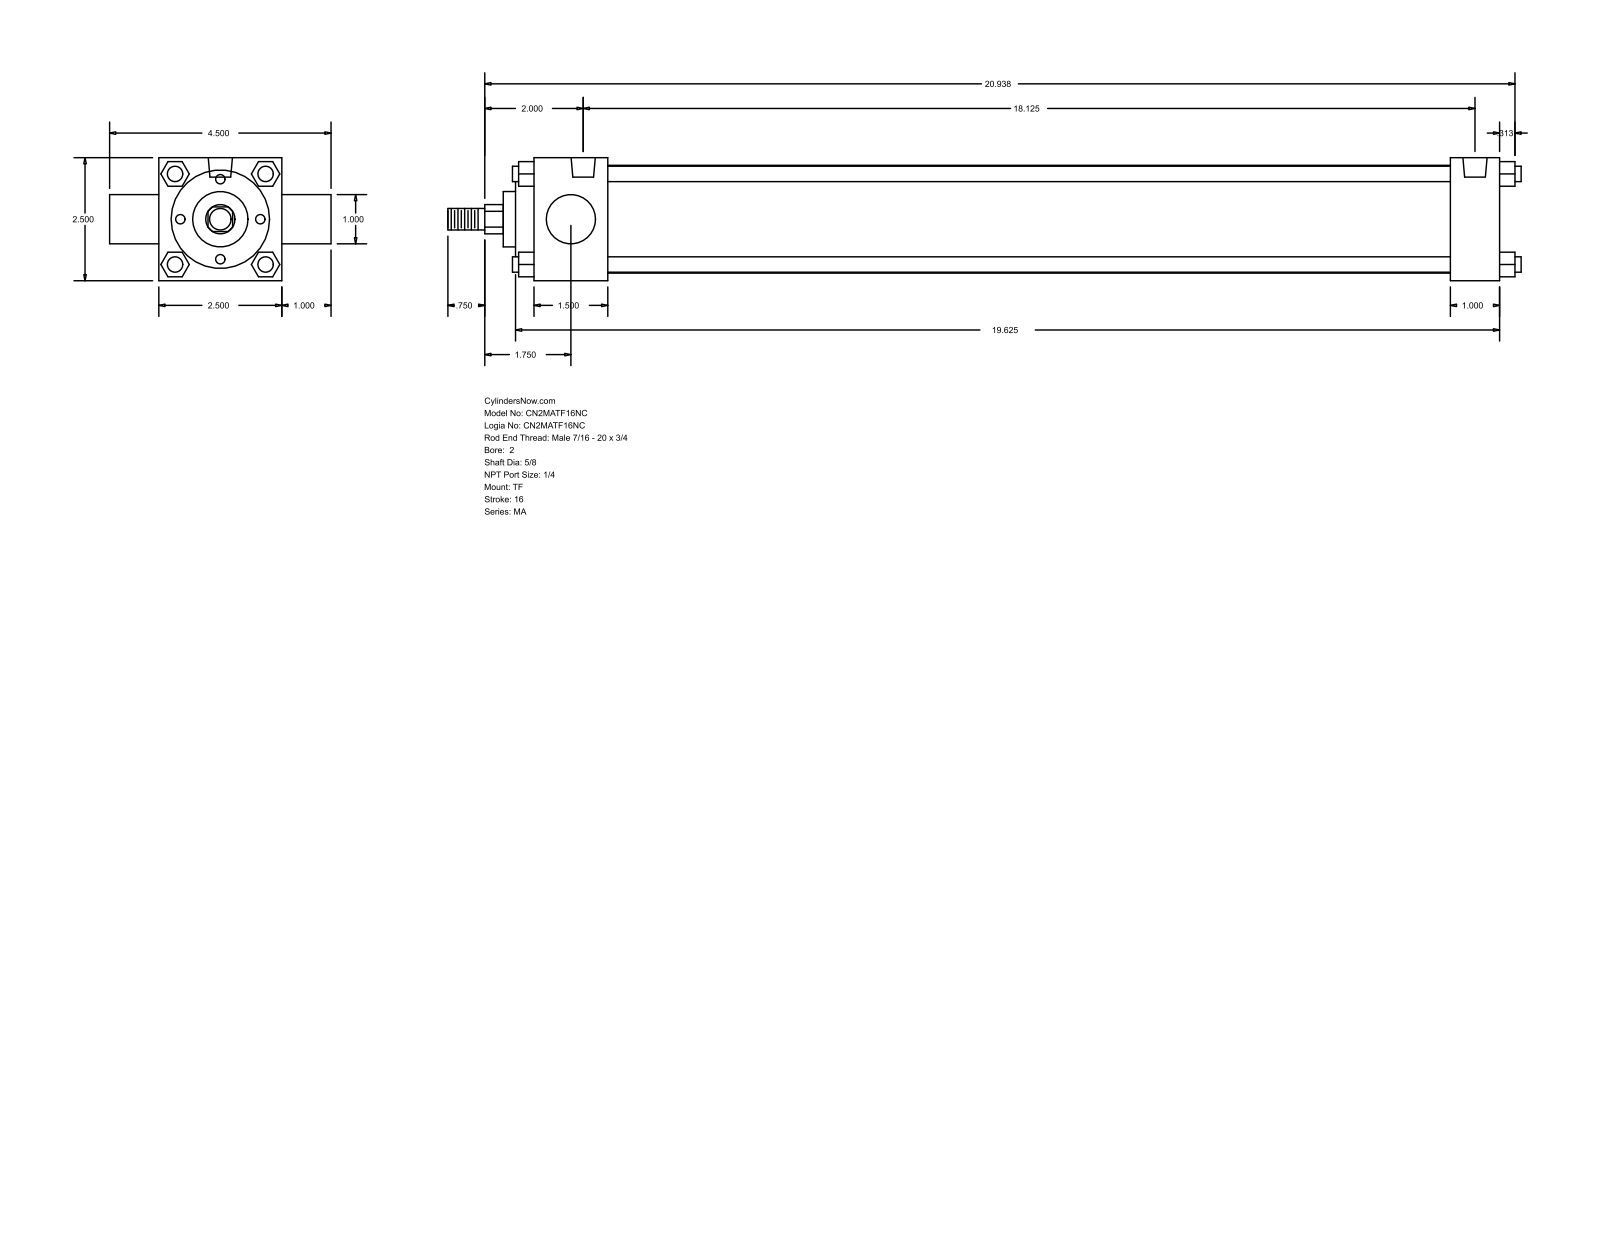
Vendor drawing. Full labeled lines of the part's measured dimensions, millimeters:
Part name (STEP PRODUCT): MA_TF__0200_0.625
STEP written by: GSSL Pune (CONFIG_CONTROL_DESIGN)
Units: millimetres
Bodies: 0 solids, 122 faces (93 planar, 29 cylindrical, 0 other)
Overall size (bounding box): 554.04 × 114.3 × 63.5
Round holes (diameter × count): ⌀7.94 ×3, ⌀12.49 ×2
Round bosses / shafts (diameter × count): ⌀7.94 ×4, ⌀55.63 ×1, ⌀50.8 ×1, ⌀28.57 ×1, ⌀25.4 ×1, ⌀15.88 ×1, ⌀11.11 ×1
Partial cylindrical surfaces — rounded edges, fillets, slot ends (radius × count): R7.54 ×1
Main face-to-face distances: 63.5, 25.4, 38.1, 498.48, 12.7, 473.08, 434.98, 460.38, 9.52, 47.62
Hole centre spacings: 460.38
